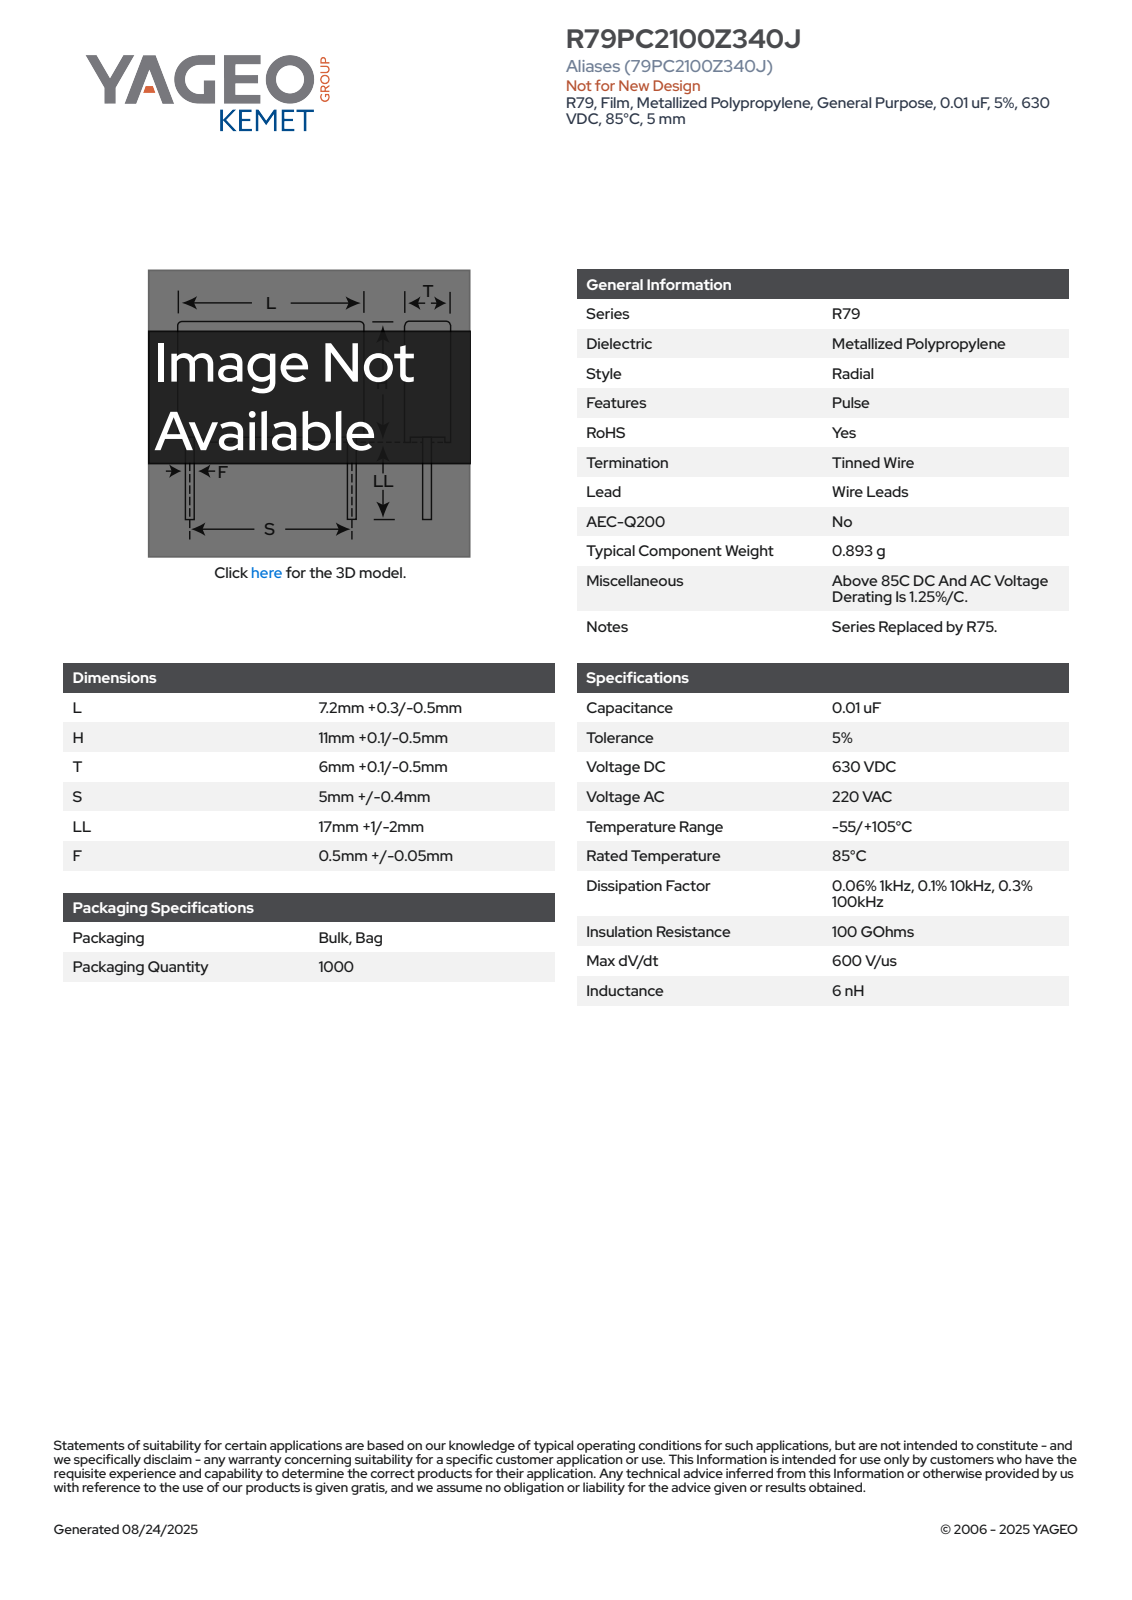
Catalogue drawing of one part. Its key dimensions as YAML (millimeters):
part_name: "CFR_RB2_7.2X11X6_L7.5H11.1T6.1S5LL18F0.55"
step_written_by: "SolidWorks 2021 (AUTOMOTIVE_DESIGN)"
units: millimeters
bodies: {solids: 4, faces: 85, planar: 77, cylindrical: 8, other: 0}
overall_size: [29.1, 7.5, 6.11]
volume: 486
surface_area: 473
round_bosses_or_shafts:
  - {diameter: 0.55, count: 2}
partial_cylinders:
  - {radius: 0.5, count: 4}
face_to_face_distances: [6.1, 7.5, 10.35, 5.85, 7.25, 0.75, 11.1, 5.6, 7, 0.38]
